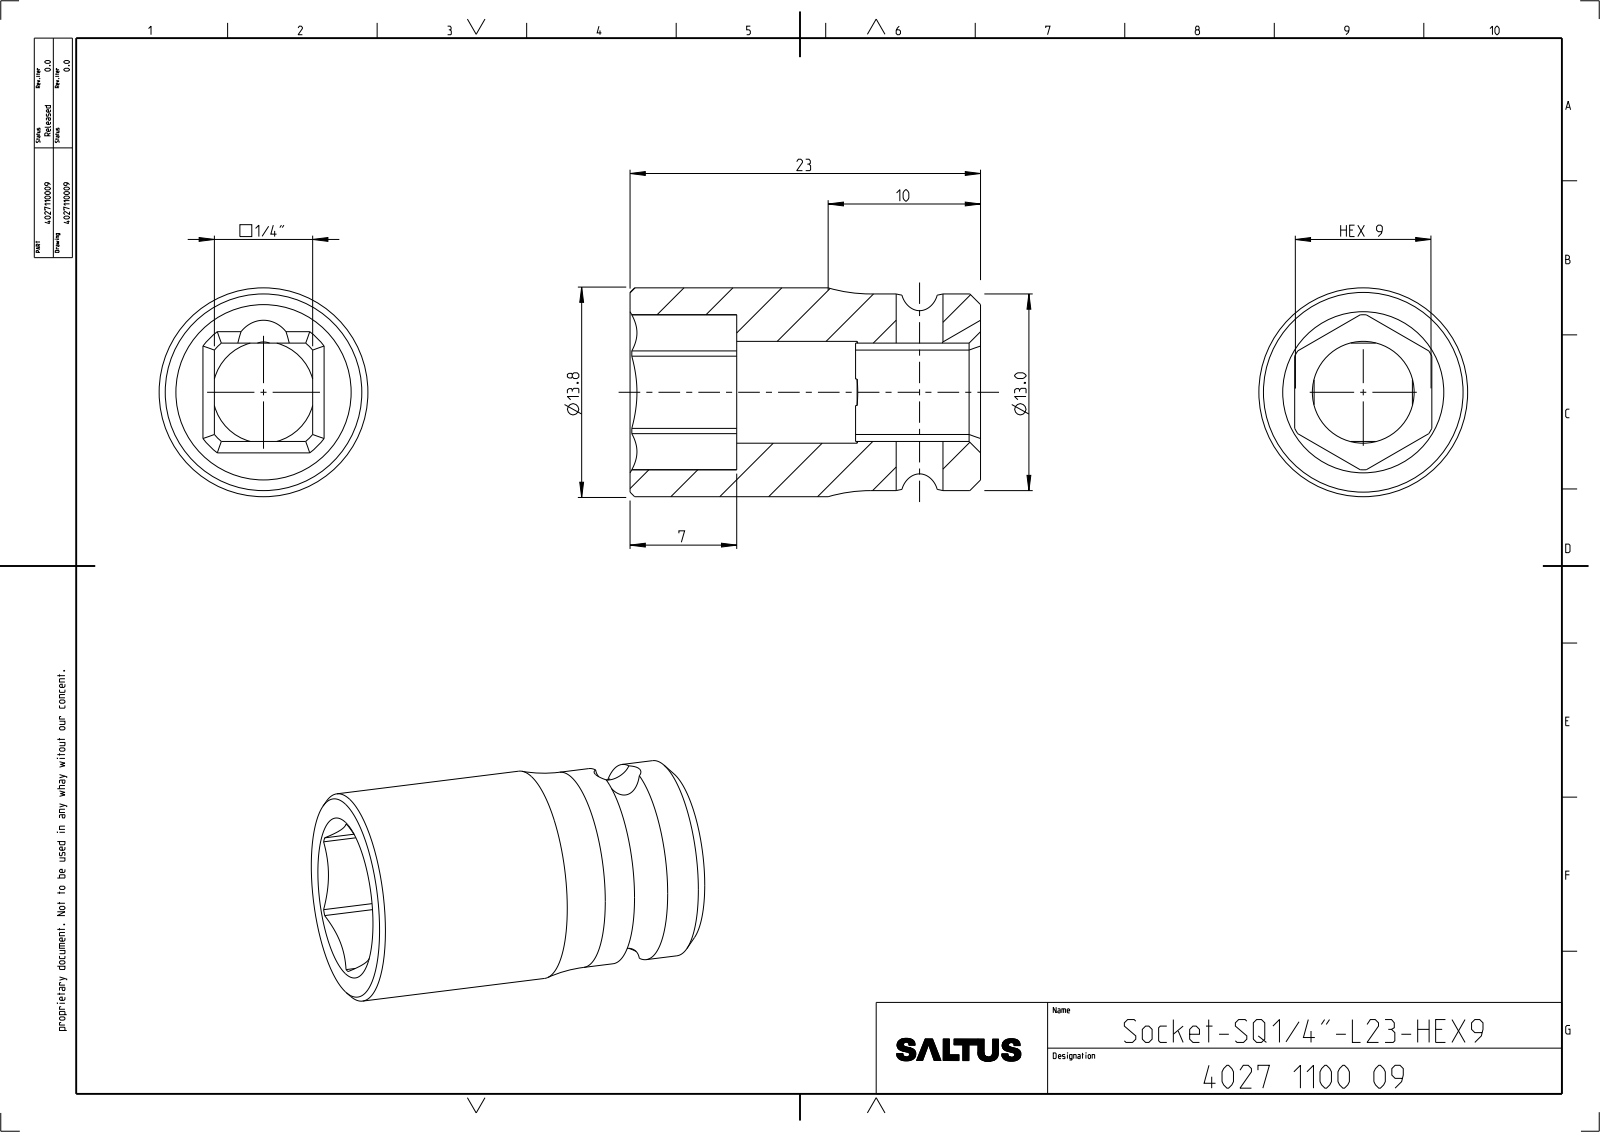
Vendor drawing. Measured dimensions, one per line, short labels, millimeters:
name: 4027110009
written by: CREO PARAMETRIC BY PTC INC, 2022414 (CONFIG_CONTROL_DESIGN)
unit: mm
bodies: 1 solid, 63 faces (22 planar, 23 cylindrical, 18 other)
size: 23 × 13.7 × 13.7
volume: 2 016 mm³; area: 1 759 mm²
holes: 1× ⌀3.07, 1× ⌀6.68
bosses: 1× ⌀13.7, 1× ⌀12.9
rounds: 1× R2, 1× R4.25, 1× R5.08
face distances: 9, 6.46, 1.27, 7.73, 23, 16, 7, 8.2, 7.8, 14.8
